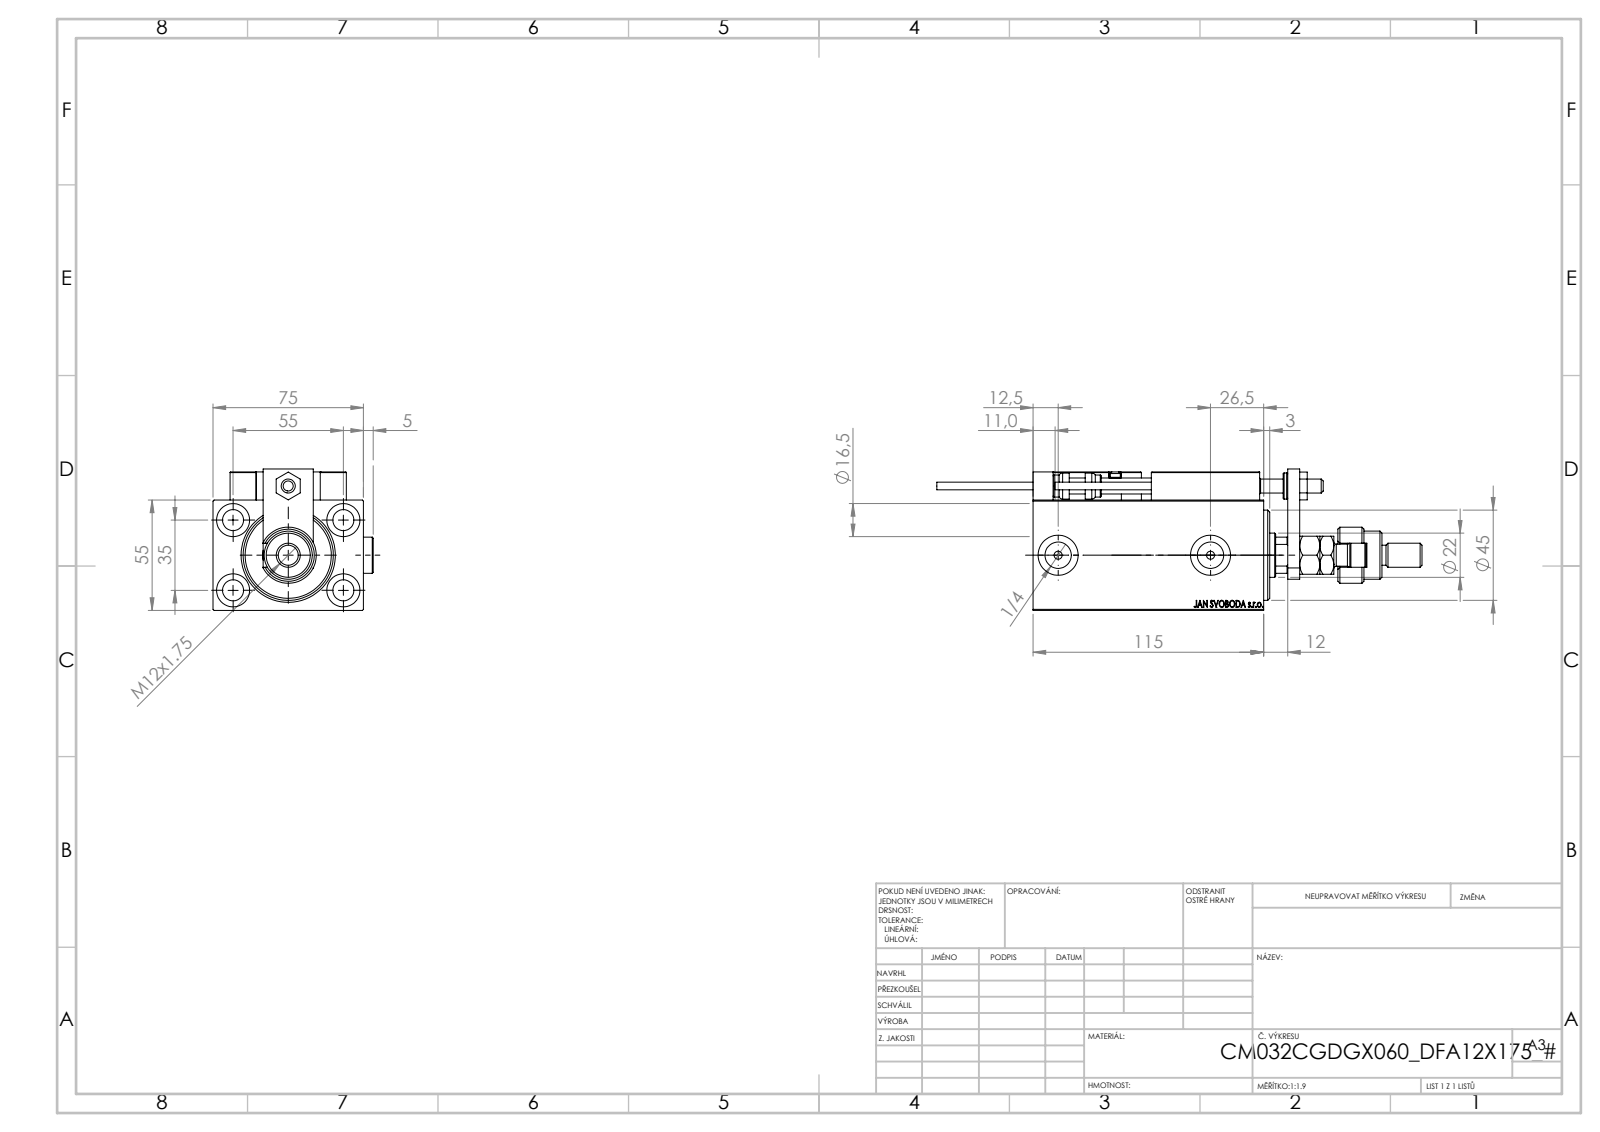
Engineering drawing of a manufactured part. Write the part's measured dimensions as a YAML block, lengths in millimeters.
part_name: "V450CM_C_VCP; MFA; NUT_D12; V450CM_C_Body (+7 more)"
step_written_by: "SolidWorks 2019 (CONFIG_CONTROL_DESIGN)"
units: millimeters
bodies: {solids: 27, faces: 1421, planar: 622, cylindrical: 217, other: 582}
overall_size: [242, 79.9, 70.5]
volume: 465748
surface_area: 117964
round_holes:
  - {diameter: 4, count: 6}
  - {diameter: 8, count: 5}
  - {diameter: 10.5, count: 5}
  - {diameter: 16.5, count: 5}
  - {diameter: 3.2, count: 4}
  - {diameter: 5, count: 2}
  - {diameter: 13.16, count: 2}
  - {diameter: 20, count: 2}
  - {diameter: 7, count: 1}
  - {diameter: 22, count: 1}
  - {diameter: 25.5, count: 1}
  - {diameter: 32, count: 1}
round_bosses_or_shafts:
  - {diameter: 18, count: 3}
  - {diameter: 11, count: 2}
  - {diameter: 5, count: 2}
  - {diameter: 3.8, count: 2}
  - {diameter: 28, count: 1}
  - {diameter: 24, count: 1}
  - {diameter: 13, count: 1}
  - {diameter: 12, count: 1}
partial_cylinders:
  - {radius: 0.3, count: 30}
  - {radius: 3, count: 2}
  - {radius: 9.75, count: 1}
  - {radius: 10.5, count: 1}
face_to_face_distances: [55, 75, 14, 12, 10, 5, 18, 25, 6, 7]
hole_center_spacings: [32.6, 11.37, 20, 29.59, 29.69, 32.33, 35, 36.06]
